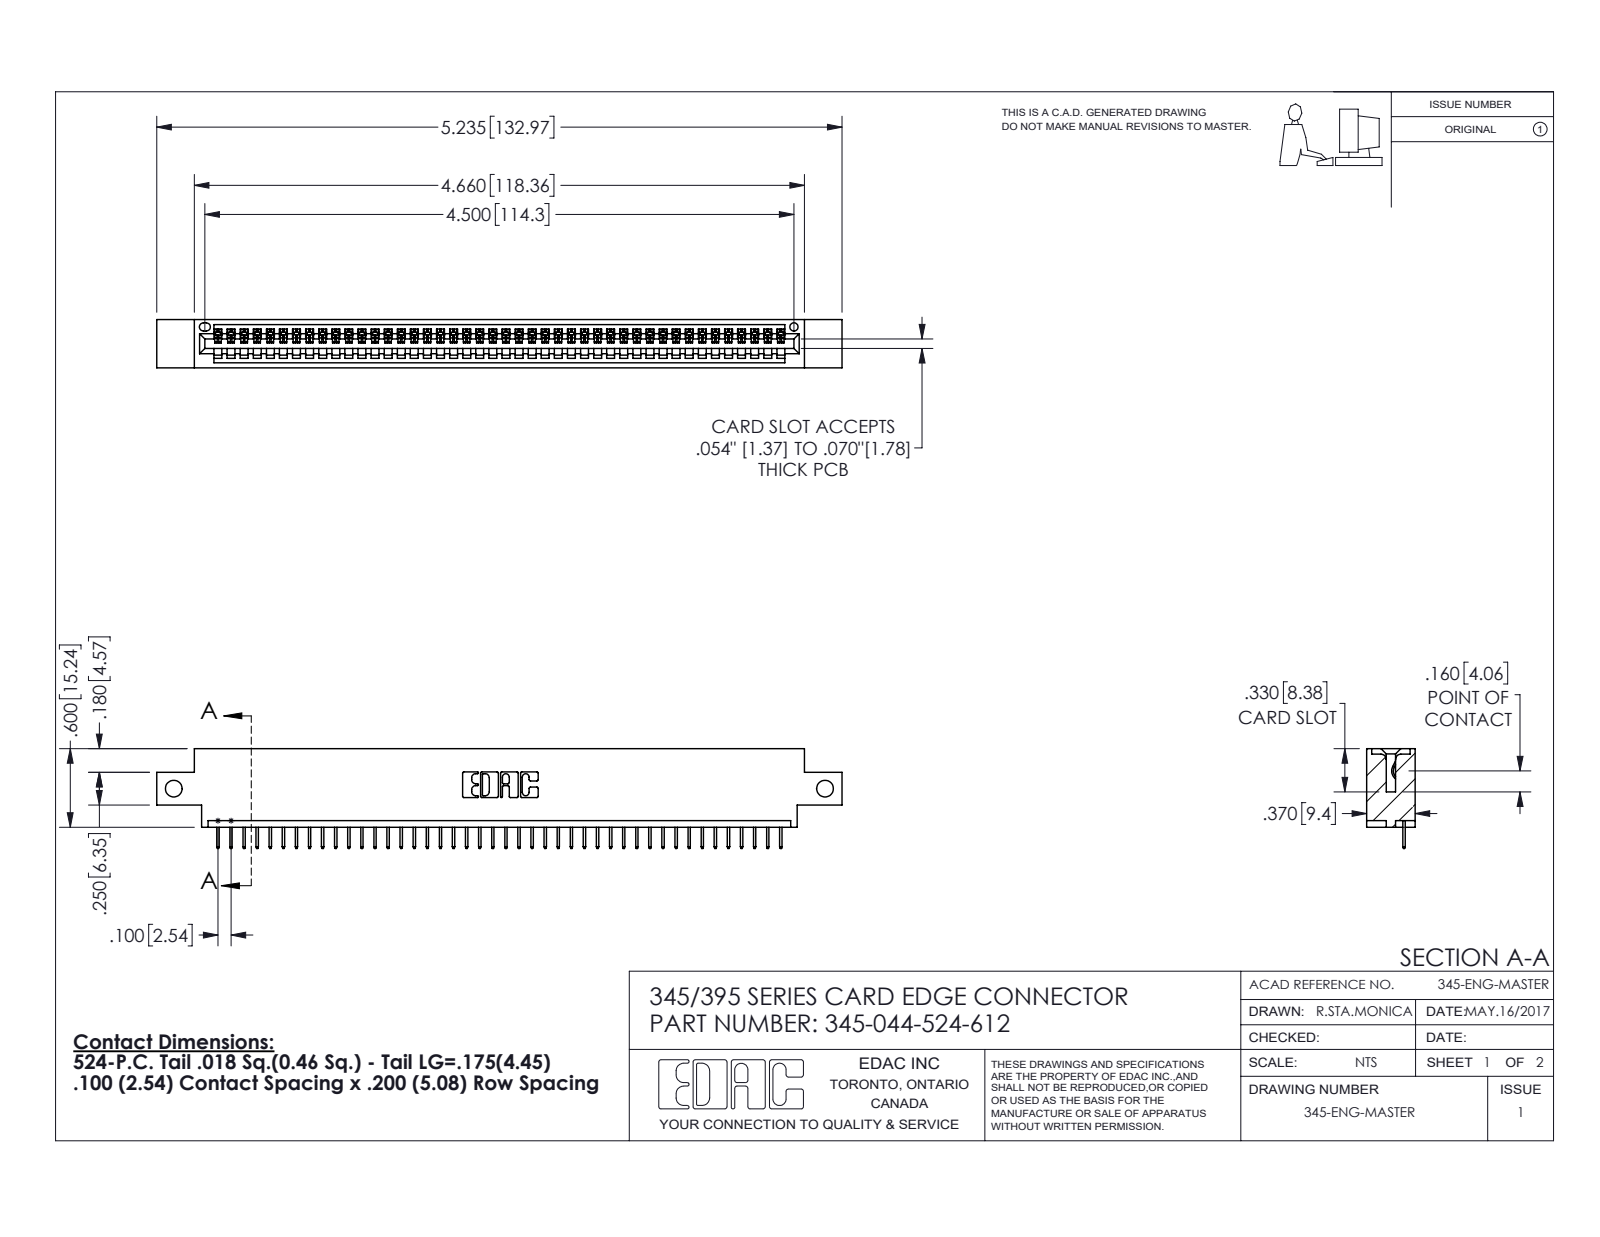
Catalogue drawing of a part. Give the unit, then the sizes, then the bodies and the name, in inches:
Units: inches
Overall size (bounding box): 5.235 × 0.762 × 0.37
Round holes (diameter × count): ⌀0.128 ×2, ⌀0.064 ×1
Partial cylindrical surfaces — rounded edges, fillets, slot ends (radius × count): R0.006 ×88, R0.01 ×22, R0.007 ×6, R0.031 ×6, R0.026 ×3, R0.031 ×2, R0.04 ×2, R0.014 ×1
Main face-to-face distances: 0.072, 0.298, 0.37, 0.2, 0.098, 0.272, 0.025, 0.225, 0.072, 0.175
Hole centre spacings: 4.975
Volume: 0.749 in³ · Surface area: 24.43 in²
Bodies: 45 solids, 2858 faces (2108 planar, 750 cylindrical, 0 other)
Part name (STEP PRODUCT): 345-044-524-612; 345-292-001_345-293-124; 345 Part_0.170 Offset - Side Mount
STEP written by: SolidWorks 2016 (CONFIG_CONTROL_DESIGN)
